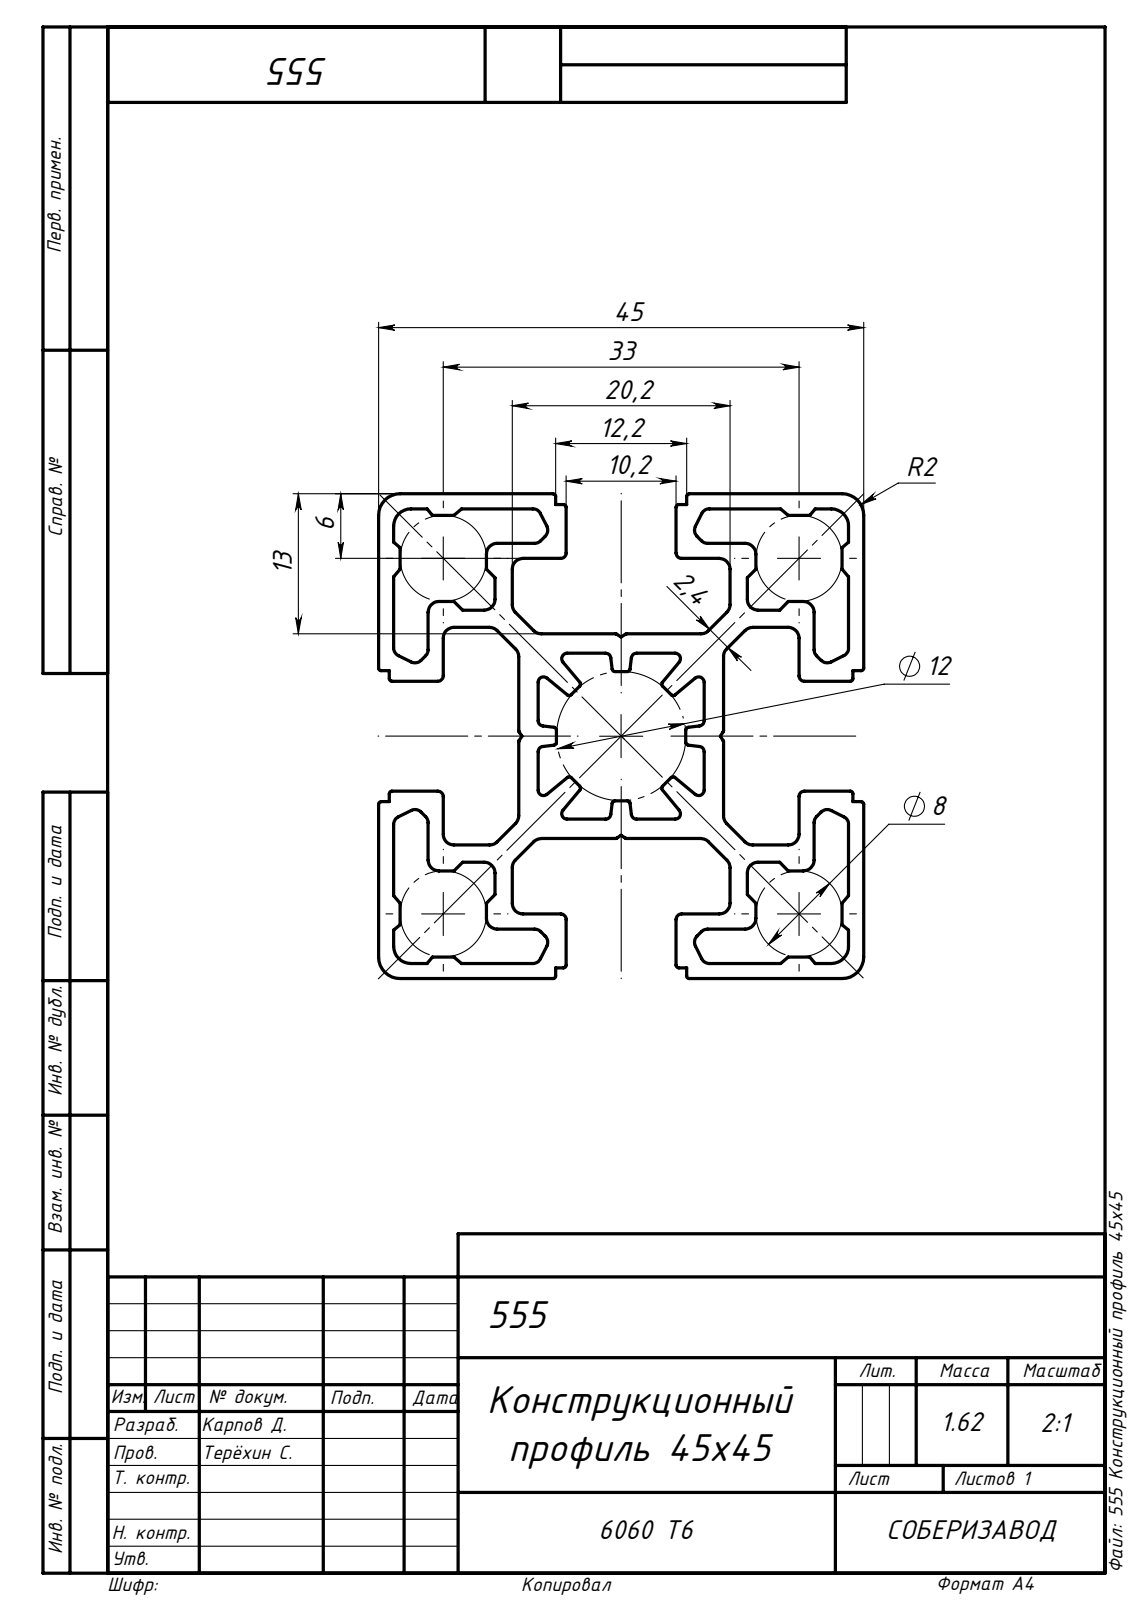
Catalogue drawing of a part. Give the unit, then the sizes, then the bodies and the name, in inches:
Units: inches
Overall size (bounding box): 39.37 × 1.772 × 1.772
Partial cylindrical surfaces — rounded edges, fillets, slot ends (radius × count): R0.01 ×40, R0.039 ×36, R0.02 ×24, R0.031 ×24, R0.063 ×4, R0.079 ×4
Main face-to-face distances: 0.055, 0.504, 1.205, 1.717, 1.772, 0.181, 1.535, 0.512, 1.26, 0.457
Volume: 36.63 in³ · Surface area: 1 013 in²
Bodies: 1 solid, 350 faces (194 planar, 156 cylindrical, 0 other)
Part name (STEP PRODUCT): 555 Конструкционный профиль 45х45
STEP written by: SolidWorks 2017 (AUTOMOTIVE_DESIGN)
